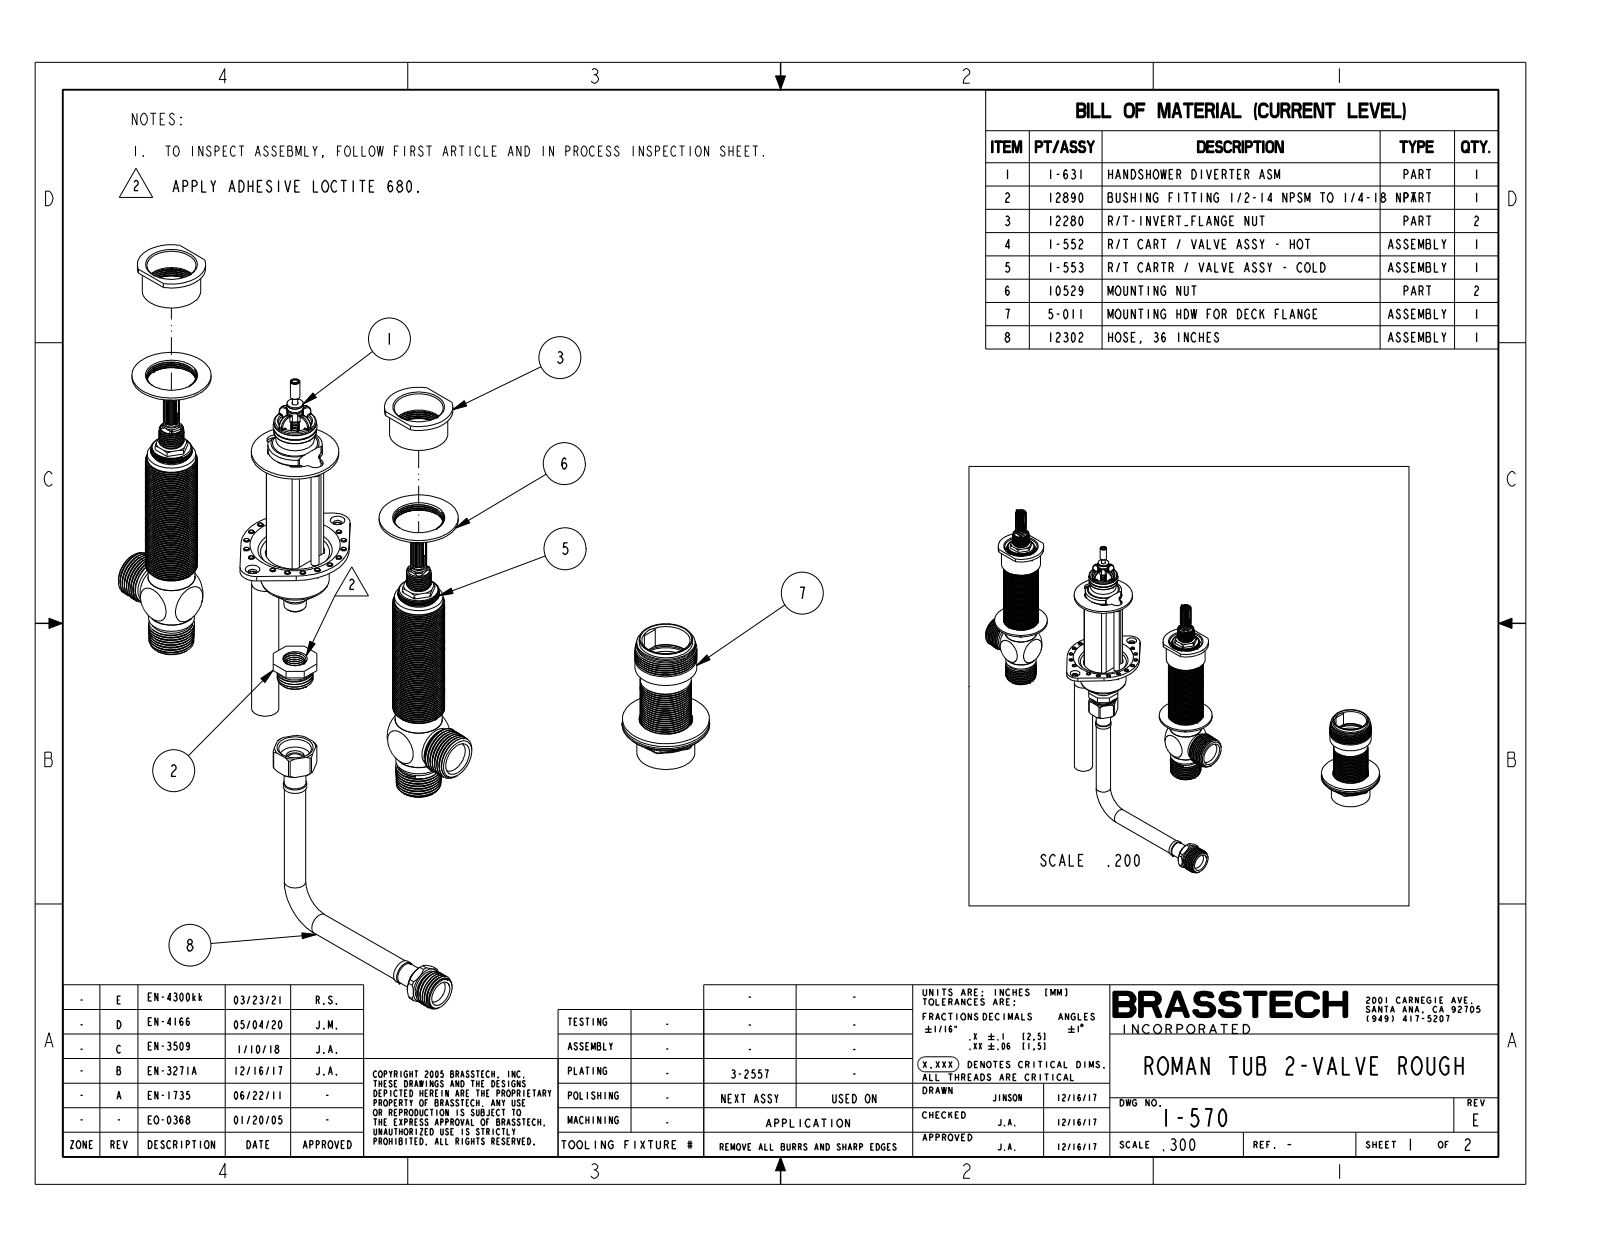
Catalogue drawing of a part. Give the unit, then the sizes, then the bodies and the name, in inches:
Units: inches
Overall size (bounding box): 18.26 × 11.343 × 3.25
Round holes (diameter × count): ⌀0.115 ×18, ⌀1.12 ×3, ⌀0.196 ×2, ⌀0.201 ×2, ⌀0.236 ×2, ⌀0.276 ×2, ⌀0.132 ×1, ⌀0.135 ×1, ⌀0.14 ×1, ⌀0.168 ×1, ⌀0.175 ×1, ⌀0.177 ×1
Round bosses / shafts (diameter × count): ⌀2 ×2, ⌀1.811 ×2, ⌀1.335 ×2, ⌀1.187 ×2, ⌀1.11 ×2, ⌀1.075 ×2, ⌀1.047 ×2, ⌀0.945 ×2
Partial cylindrical surfaces — rounded edges, fillets, slot ends (radius × count): R0.02 ×16, R0.04 ×14, R0.03 ×12, R0.05 ×12, R0.08 ×8, R0.15 ×6, R0.01 ×4, R0.07 ×4
Main face-to-face distances: 3, 0.125, 0.98, 1.437, 1.563, 0.061, 1.498, 3.061, 0.05, 1.548
Hole centre spacings: 0.352, 0.695, 1.125, 1.591, 1.022, 1.322, 1.82, 2.005
Volume: 26.21 in³ · Surface area: 218.4 in²
Bodies: 5 solids, 1995 faces (405 planar, 835 cylindrical, 755 other)
Part name (STEP PRODUCT): 1-570
STEP written by: CREO PARAMETRIC BY PTC INC, 2018400 (AUTOMOTIVE_DESIGN)
